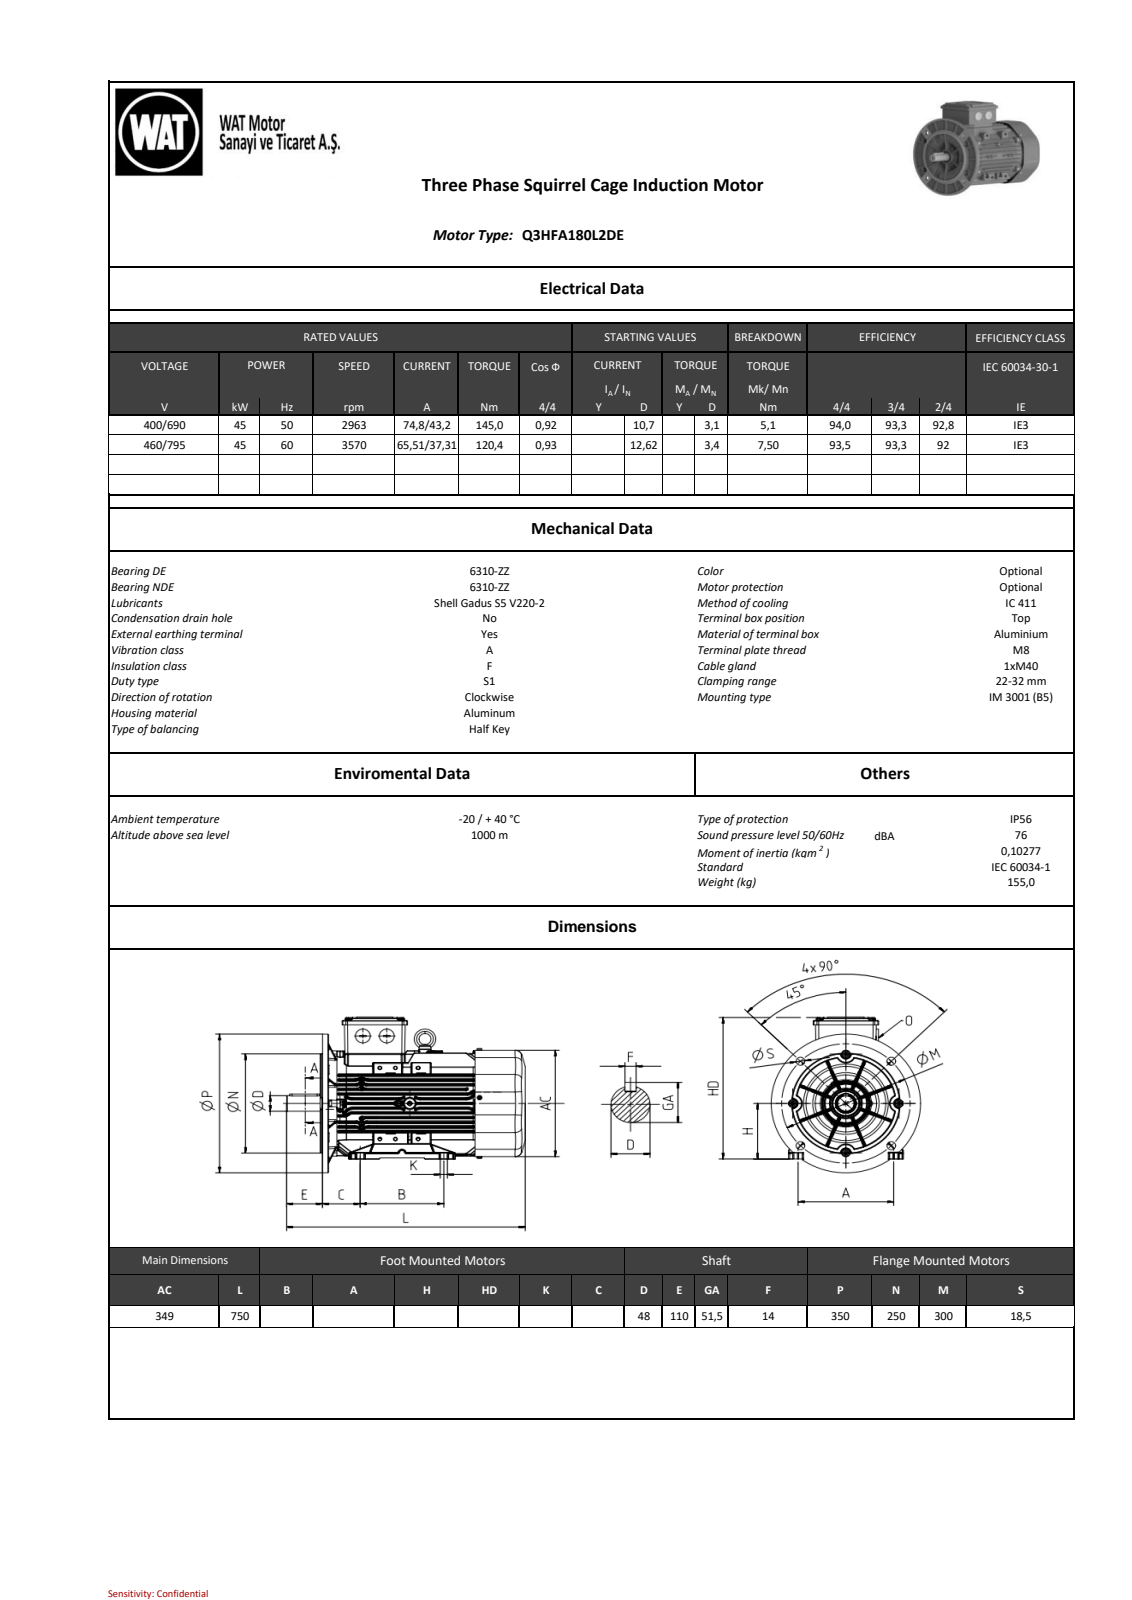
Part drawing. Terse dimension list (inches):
name: 001_objects
written by: SIEMENS PLM Software NX2206.8101 (AP203_CONFIGURATION_CONTROLLED_3D_DESIGN_OF_MECHANICAL_PARTS_AND_ASSEMBLIES_MIM_LF)
unit: in
bodies: 0 solids, 6019 faces (2162 planar, 2061 cylindrical, 1796 other)
size: 29.508 × 16.838 × 13.833
holes: 4× ⌀0.22, 4× ⌀0.669, 4× ⌀0.728, 2× ⌀0.866, 2× ⌀0.986, 1× ⌀0.217, 1× ⌀0.262, 1× ⌀0.315, 1× ⌀2.008, 1× ⌀3.15, 1× ⌀3.228, 1× ⌀4.331
bosses: 3× ⌀0.374, 2× ⌀2.165, 2× ⌀2.016, 2× ⌀0.984, 2× ⌀0.512, 1× ⌀11.929, 1× ⌀9.843, 1× ⌀3.424
rounds: 638× R0.079, 556× R0.039, 90× R0.197, 44× R0.118, 40× R0.157, 22× R0.315, 21× R0.02, 18× R0.039
face distances: 0.047, 0.638, 1.279, 0.641, 6.734, 6.844, 5.565, 6.206, 6.184, 5.546
hole spacings: 4.703, 11.313, 5.906, 6.339, 8.352, 8.964, 11.811, 12.677
